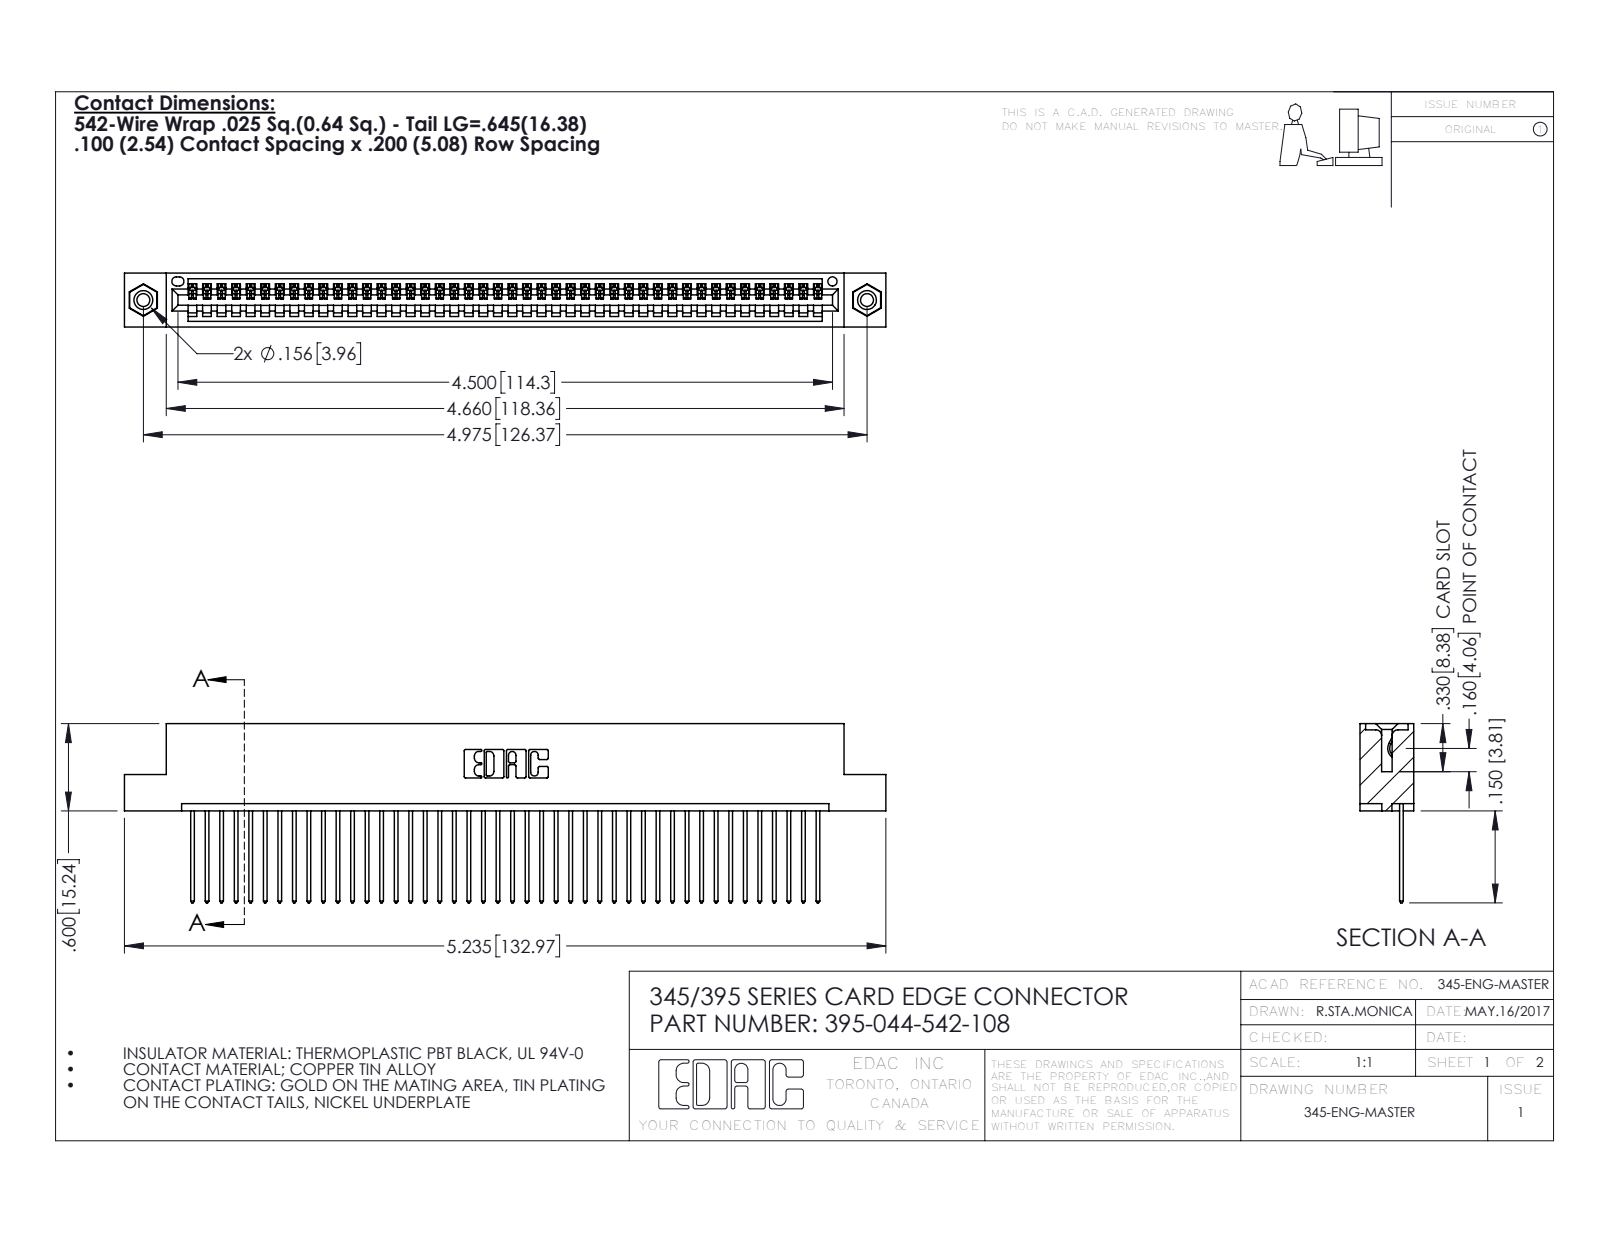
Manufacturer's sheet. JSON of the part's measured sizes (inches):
{"part_name": "345-292-001_345-293-142; 345-250-001_345-250-003-102; 395-044-542-108; 345 Part_Flush Mounting Lugs - 0.156 Dia-TI", "step_written_by": "SolidWorks 2016 (CONFIG_CONTROL_DESIGN)", "units": "inches", "bodies": {"solids": 47, "faces": 2738, "planar": 1872, "cylindrical": 850, "other": 16}, "overall_size": [5.235, 1.232, 0.37], "volume_in3": 0.777, "surface_area_in2": 27.27, "round_holes": [[0.089, 2], [0.125, 2], [0.156, 2], [0.064, 1]], "round_bosses_or_shafts": [[0.155, 2]], "partial_cylinders_radius": [[0.006, 88], [0.01, 88], [0.01, 22], [0.007, 6], [0.031, 6], [0.026, 3], [0.031, 2], [0.04, 2]], "face_to_face_distances": [0.072, 0.298, 0.37, 0.098, 0.272, 0.025, 0.2, 0.225, 0.149, 0.072], "hole_center_spacings": [0.27, 4.739, 4.975]}
